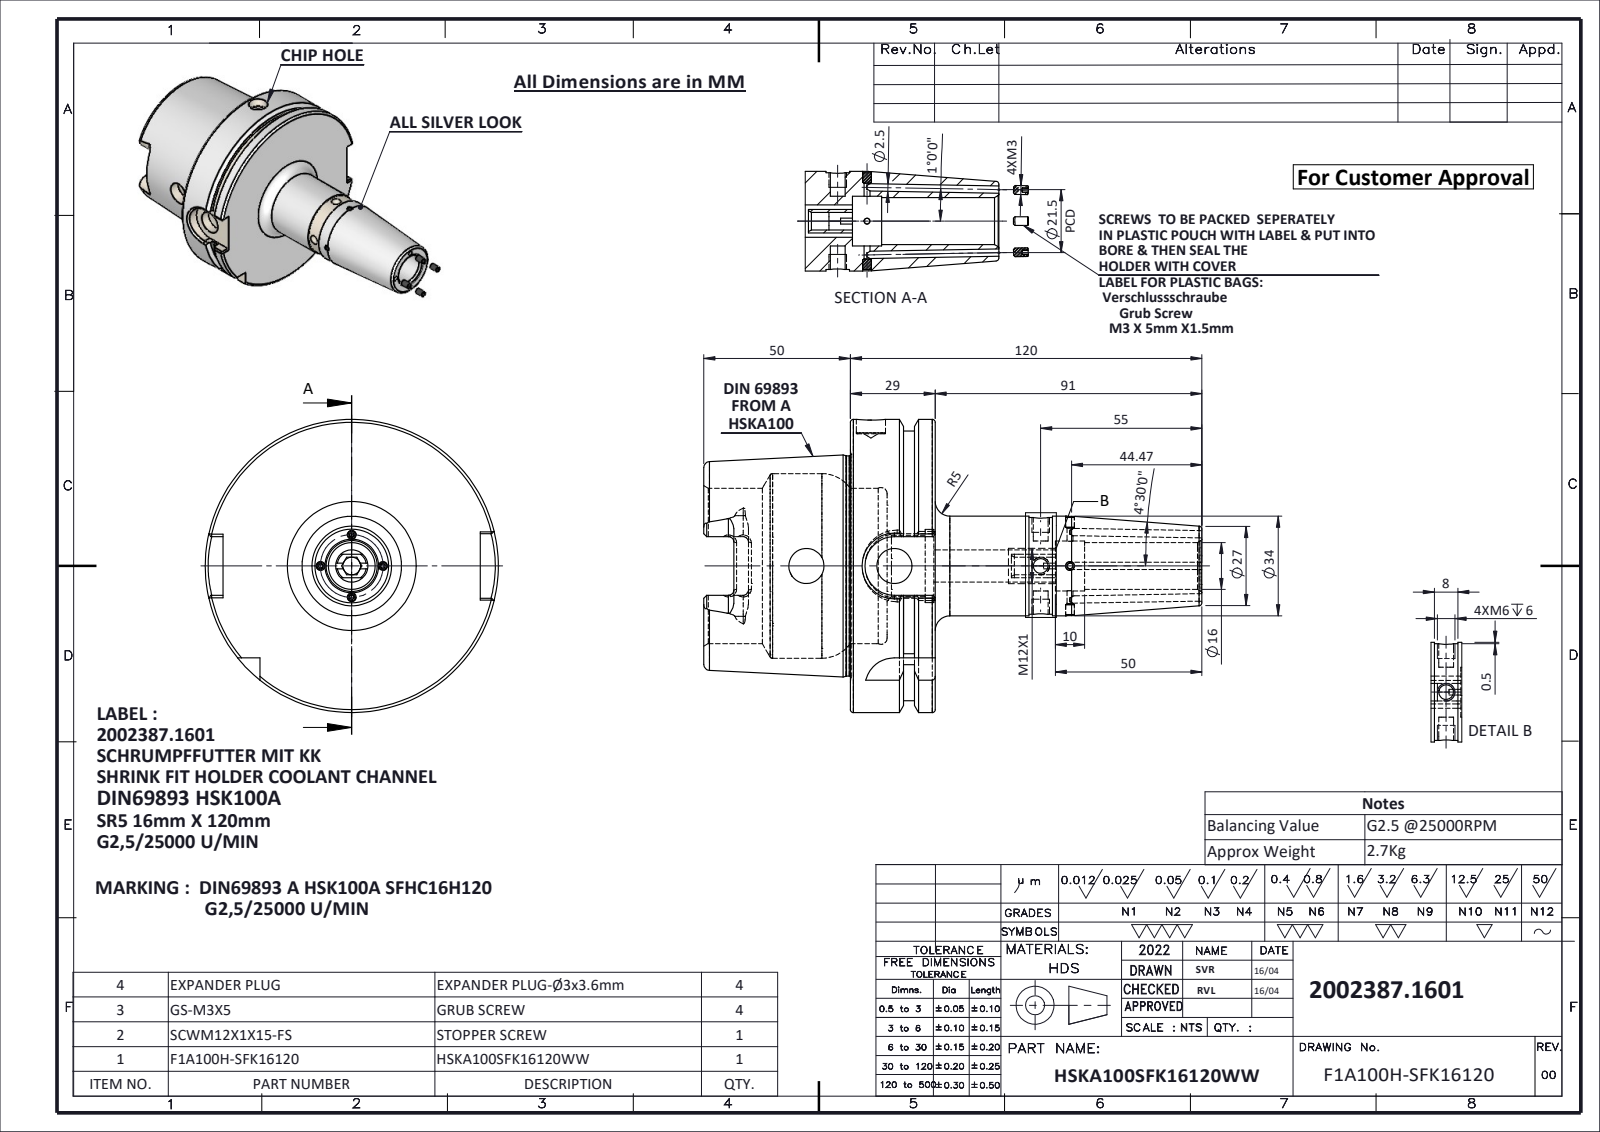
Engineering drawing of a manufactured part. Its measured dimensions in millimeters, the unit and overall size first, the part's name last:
Units: millimetres
Overall size (bounding box): 179.97 × 100 × 100
Round holes (diameter × count): ⌀2.5 ×4, ⌀2 ×2, ⌀3 ×2, ⌀5 ×2, ⌀12 ×2, ⌀6 ×1, ⌀10 ×1, ⌀11 ×1, ⌀16 ×1, ⌀17 ×1, ⌀21 ×1, ⌀25 ×1
Round bosses / shafts (diameter × count): ⌀3 ×4, ⌀100 ×1, ⌀92 ×1, ⌀75.16 ×1, ⌀34 ×1, ⌀33 ×1
Partial cylindrical surfaces — rounded edges, fillets, slot ends (radius × count): R1.8 ×6, R4.88 ×4, R10 ×2, R6 ×1, R11 ×1
Main face-to-face distances: 28.95, 12.5, 16.45, 50, 62.5, 78.95, 71.87, 21.87, 9.37, 7.08
Hole centre spacings: 10, 30, 49.95, 57.95, 59.95, 67.95, 79.95, 89.95
Volume: 313 795 mm³ · Surface area: 65 908 mm²
Bodies: 10 solids, 382 faces (146 planar, 108 cylindrical, 128 other)
Part name (STEP PRODUCT): EXPANDER PLUG Ø3x3.6; SCWM12x1x15-FLAT; F1A100H-SFK16120; GS-M3X5 (+1 more)
STEP written by: SolidWorks 2024 (CONFIG_CONTROL_DESIGN)
